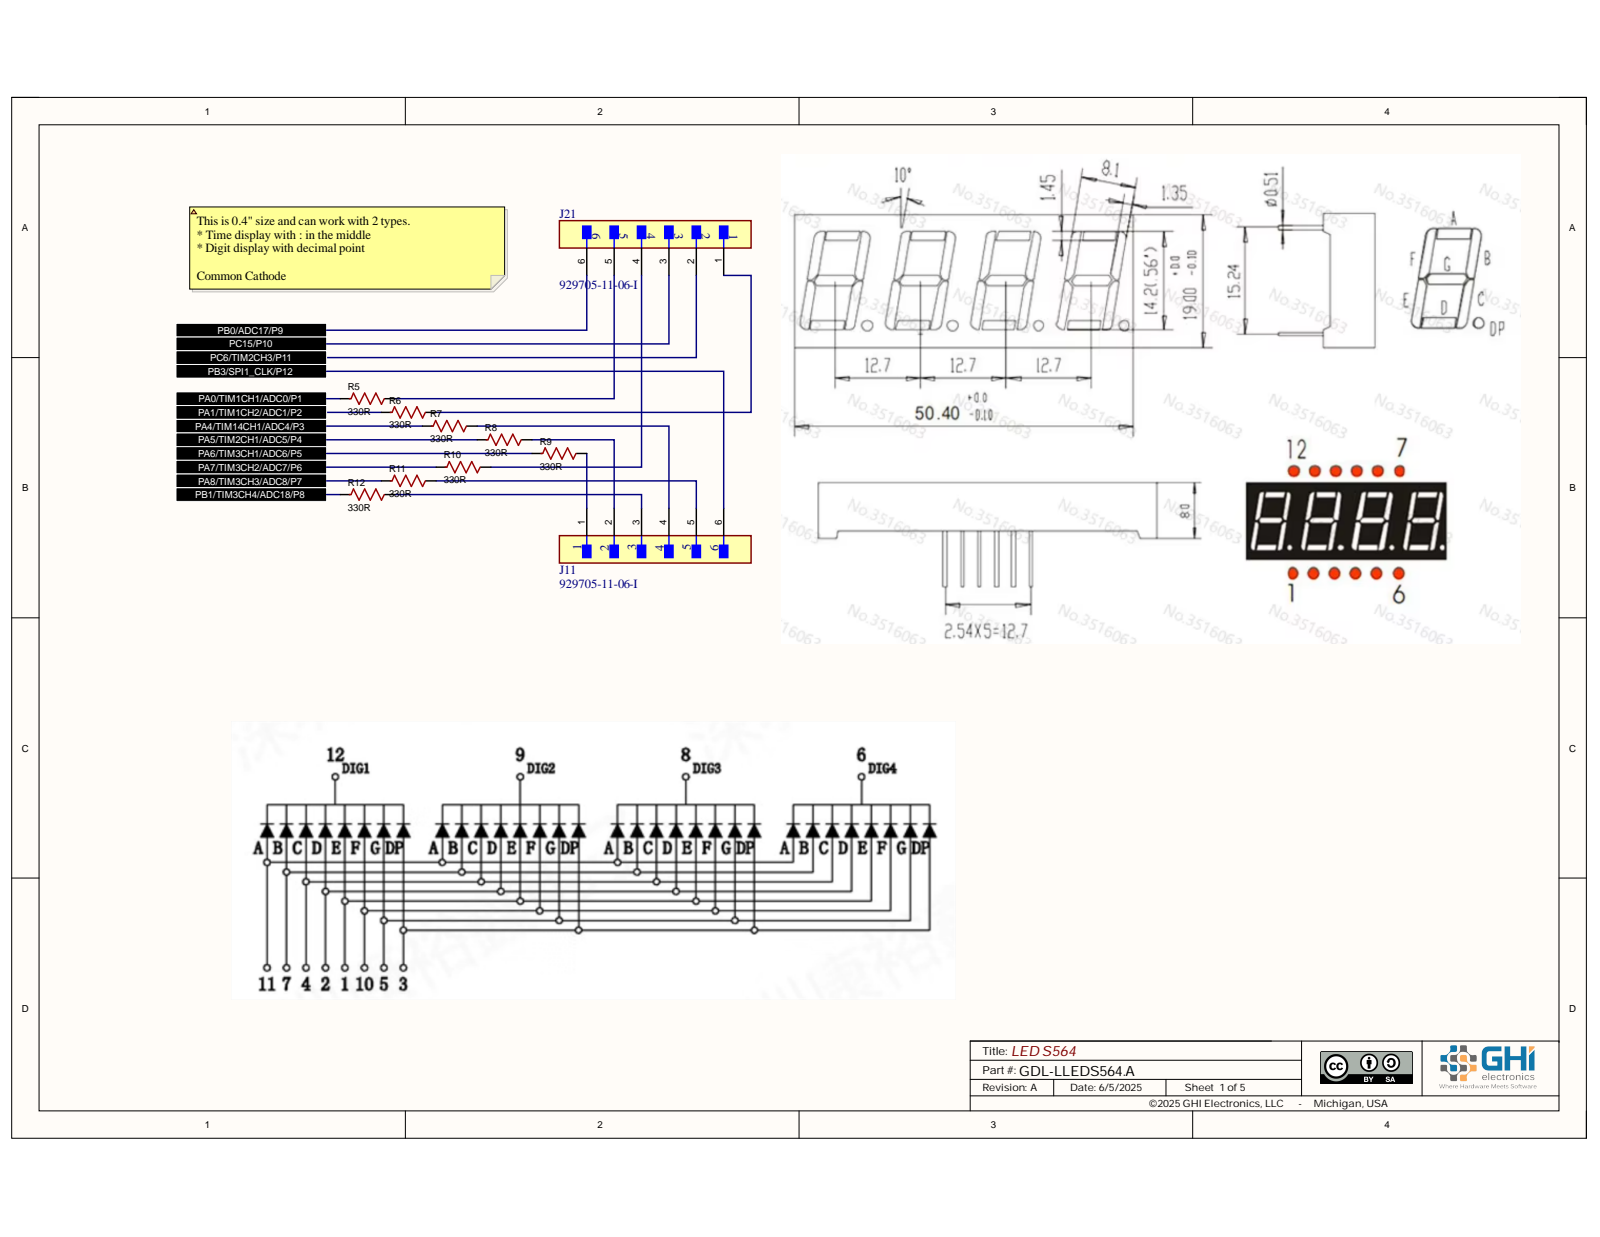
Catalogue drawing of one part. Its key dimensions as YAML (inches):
part_name: "PCB; Board; R12; User Library-R SMD 0402 (+7 more)"
step_written_by: "Open CASCADE 7.5 (AUTOMOTIVE_DESIGN)"
units: inches
bodies: {solids: 130, faces: 3609, planar: 1879, cylindrical: 930, other: 800}
overall_size: [2.638, 0.866, 0.67]
volume: 0.629
surface_area: 11.91
round_holes:
  - {diameter: 0.04, count: 12}
  - {diameter: 0.118, count: 4}
  - {diameter: 0.04, count: 2}
round_bosses_or_shafts:
  - {diameter: 0.024, count: 2}
partial_cylinders:
  - {radius: 0.005, count: 35}
  - {radius: 0.006, count: 14}
  - {radius: 0.138, count: 4}
  - {radius: 0.007, count: 2}
  - {radius: 0.007, count: 2}
  - {radius: 0.007, count: 2}
face_to_face_distances: [0.063, 0.315, 0.181, 0.496, 0.118, 0.433, 0.748, 0.025, 0.059, 0.807]
hole_center_spacings: [0.1, 0.608, 0.2, 0.632, 0.3, 0.6, 0.671, 0.4]
